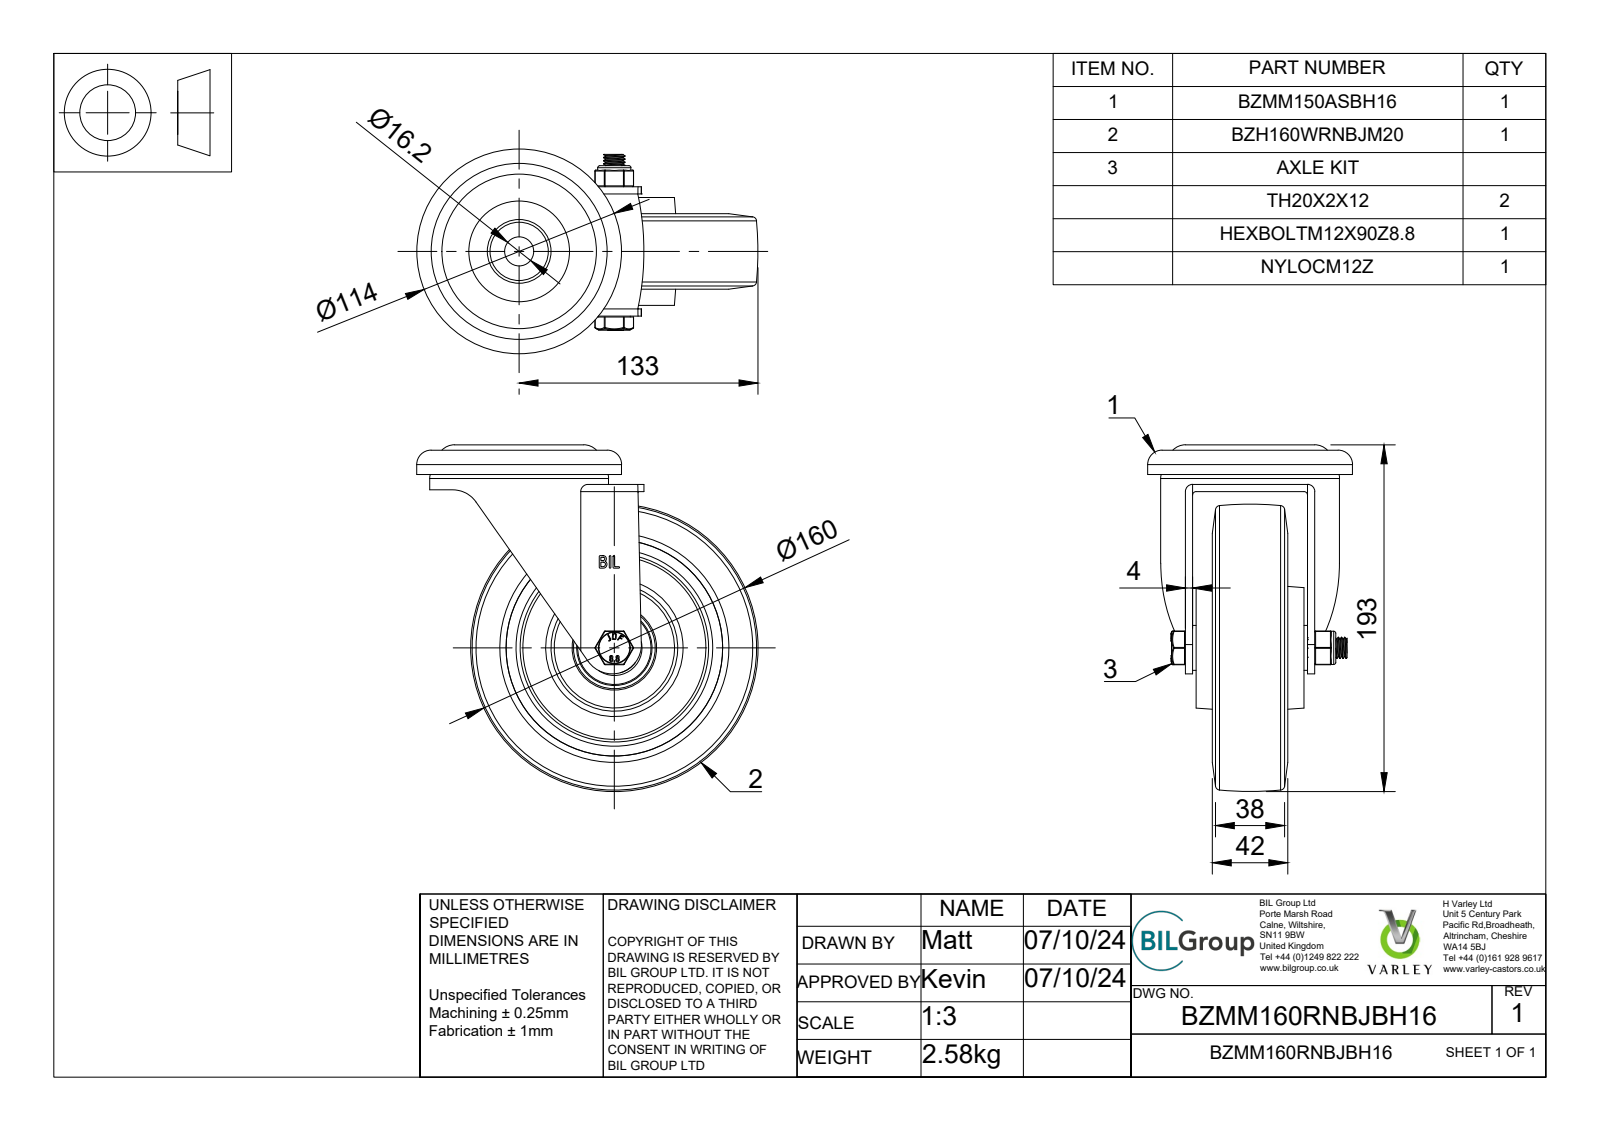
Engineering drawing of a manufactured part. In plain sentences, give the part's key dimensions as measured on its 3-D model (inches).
The part is named "BZMM160RNBJBH16 v3; BZMM150ASBH16 - 64 v1; ZINC PLATED, PRESSED STEEL HEAD; ZINC PLATED, PRESSED STEEL FORKS (+8 more)". Its 3-D file was written by "Autodesk Translation Framework v13.20.0.188 (AUTOMOTIVE_DESIGN)". It is 36 solids with 1110 faces: 468 planar, 197 cylindrical and 445 other. Overall it measures 7.598 by 7.48 by 4.488 inches. Its volume is 52.22 cubic inches and its surface area 390.7 square inches. Round holes: 1 of diameter 0.472, 1 of diameter 0.48, 1 of diameter 0.551, 1 of diameter 0.638, 1 of diameter 0.787, 1 of diameter 1.122, 1 of diameter 1.213, 1 of diameter 1.587, 1 of diameter 1.594, 1 of diameter 1.614, 1 of diameter 1.654, 1 of diameter 1.85. Round bosses or shafts: 1 of diameter 4.488, 1 of diameter 3.917, 1 of diameter 2.913, 1 of diameter 1.85, 1 of diameter 1.606, 1 of diameter 1.28, 1 of diameter 1.232, 1 of diameter 1.063. Partial cylindrical surfaces (rounded edges, fillets, slot ends): 20 of radius 0.02, 4 of radius 0.019, 4 of radius 0.035, 4 of radius 0.079, 2 of radius 0.035, 2 of radius 0.035, 2 of radius 0.157, 2 of radius 0.267. The main face-to-face distances are 1.102, 1.417, 0.669, 0.984, 0.433, 2.087, 0.315, 0.157, 1.024, 0.108.
